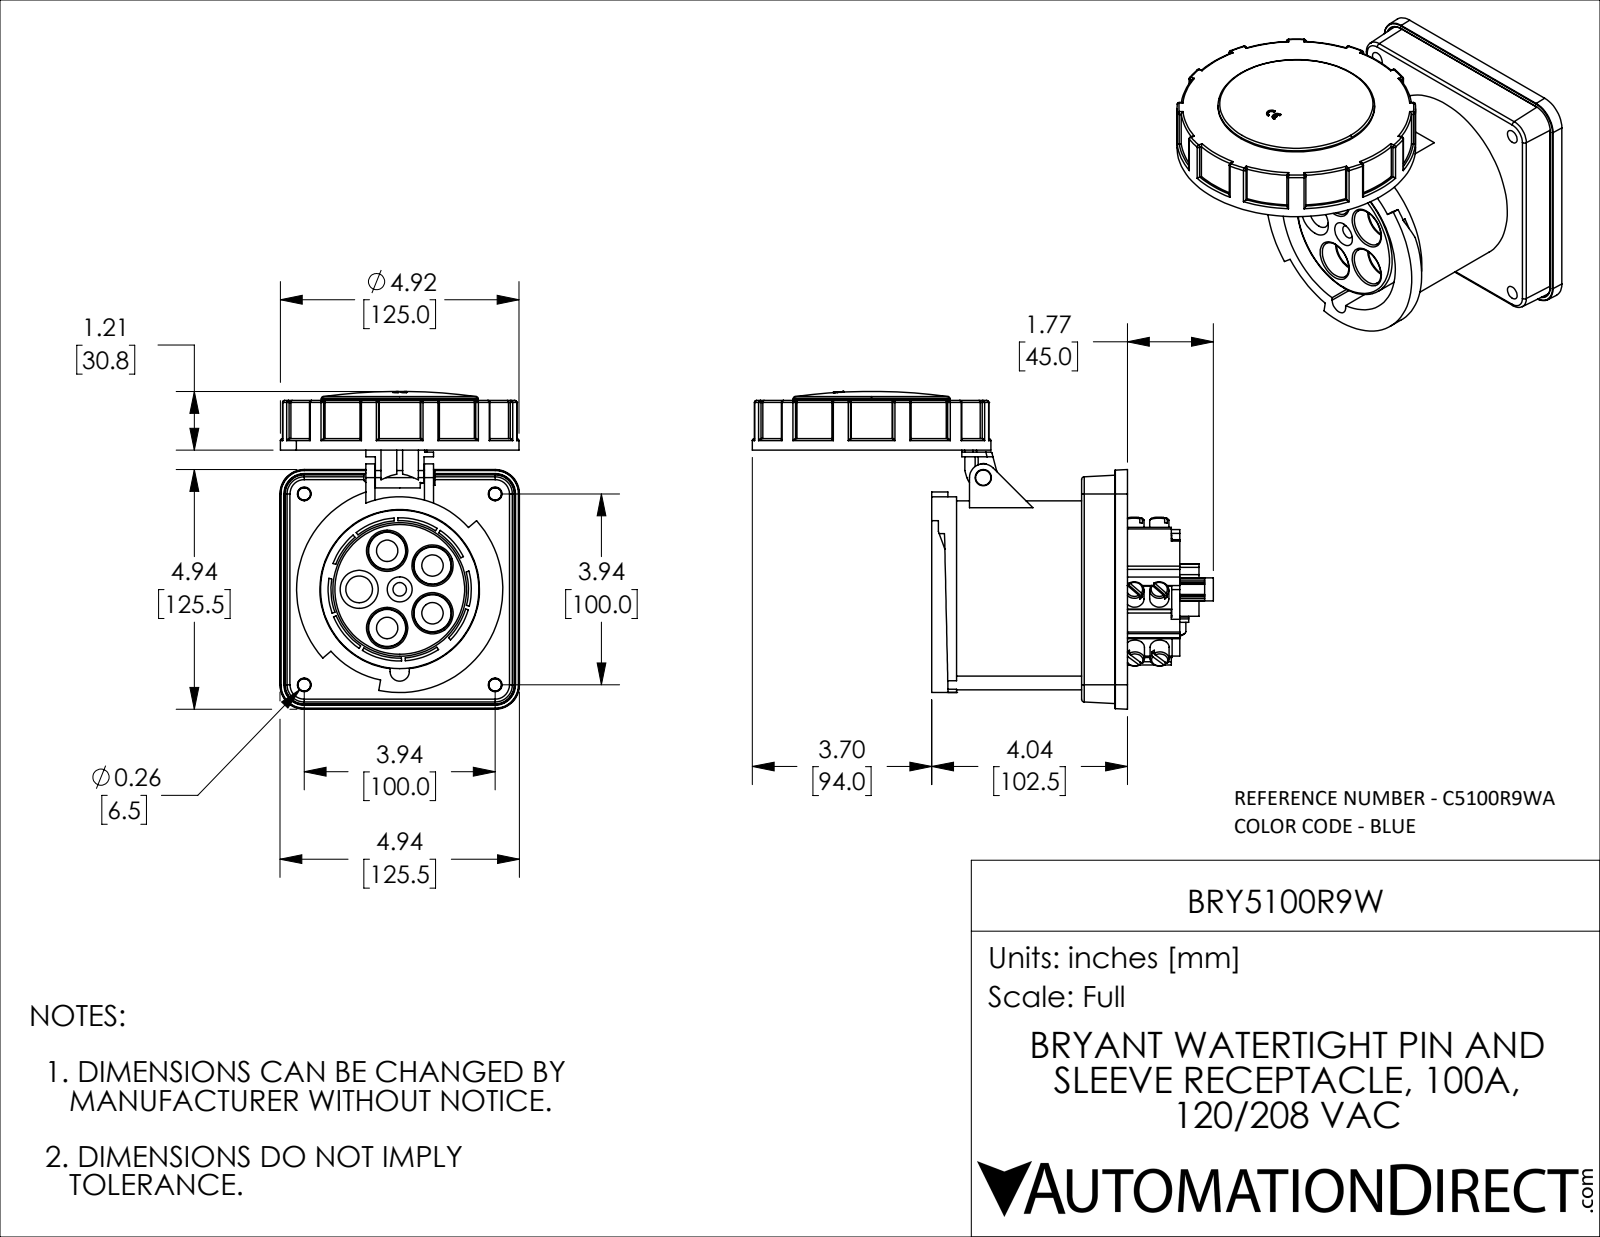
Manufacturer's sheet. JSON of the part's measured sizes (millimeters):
{"part_name": "BRY5100R9W", "step_written_by": "SolidWorks 2021 (CONFIG_CONTROL_DESIGN)", "units": "millimeters", "bodies": {"solids": 2, "faces": 1198, "planar": 513, "cylindrical": 419, "other": 266}, "overall_size": [241.5, 166.4, 125.5], "volume_mm3": 1123000, "surface_area_mm2": 183252, "round_holes": [[7.2, 4], [11.2, 4], [20, 4], [9, 3], [5.1, 1], [7.1, 1], [8.5, 1], [14, 1], [75, 1], [83.6, 1], [84, 1], [85, 1]], "round_bosses_or_shafts": [[10, 10], [125, 1], [97, 1], [92.6, 1], [83, 1], [82, 1], [80.5, 1], [72, 1]], "partial_cylinders_radius": [[1, 59], [2, 27], [2.5, 12], [4, 12], [0.25, 8], [0.5, 6], [1.01, 6], [1.28, 6]], "face_to_face_distances": [24, 23, 26, 3, 102.5, 78.5, 2, 4, 3.5, 20], "hole_center_spacings": [21.25, 24.98, 40.42, 70.71, 100, 28.84, 34.25, 14.79]}
